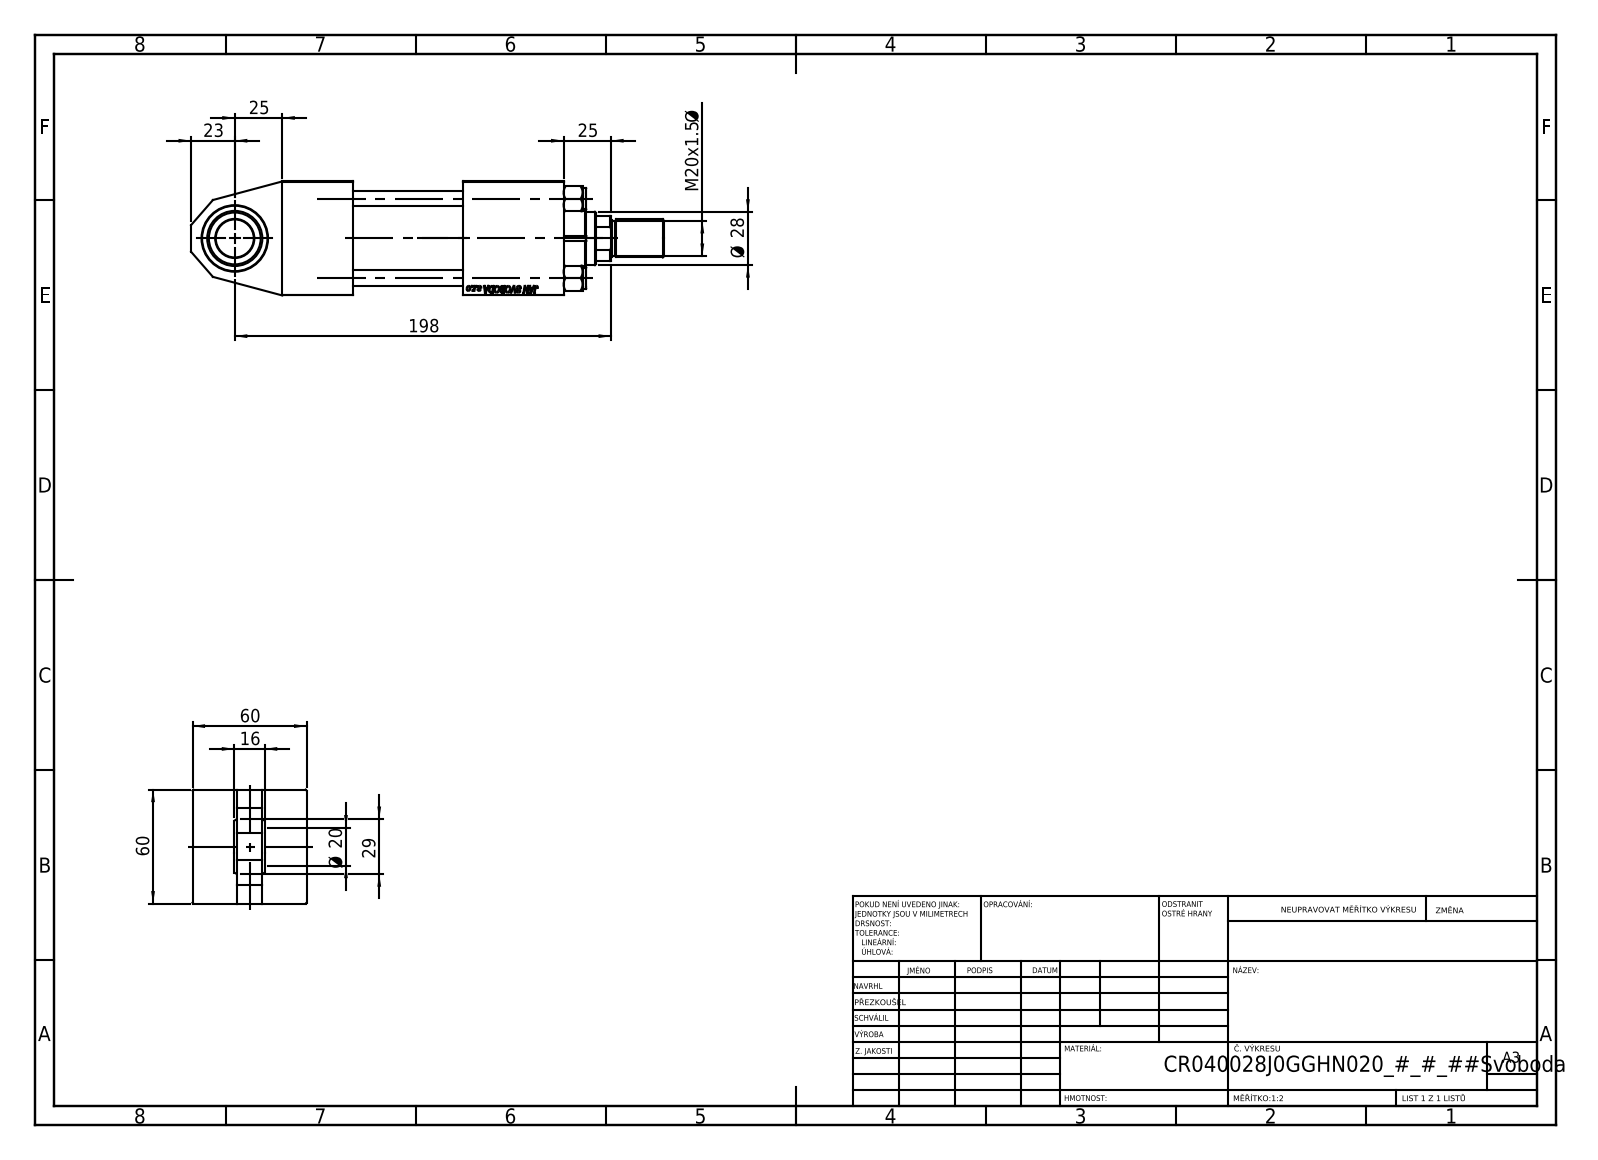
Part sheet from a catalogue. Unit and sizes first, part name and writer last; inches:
Units: inches
Overall size (bounding box): 9.803 × 2.362 × 2.362
Round holes (diameter × count): ⌀0.315 ×4, ⌀0.098 ×2, ⌀0.276 ×2, ⌀0.656 ×2, ⌀0.945 ×2, ⌀0.728 ×1, ⌀0.787 ×1, ⌀1.102 ×1, ⌀1.22 ×1, ⌀1.378 ×1, ⌀1.575 ×1, ⌀1.772 ×1
Round bosses / shafts (diameter × count): ⌀0.433 ×4, ⌀1.811 ×1, ⌀1.654 ×1, ⌀0.787 ×1, ⌀0.709 ×1
Partial cylindrical surfaces — rounded edges, fillets, slot ends (radius × count): R0.531 ×1
Main face-to-face distances: 2.362, 1.437, 0.925, 1.457, 2.087, 2.283, 3.74, 0.512, 5.827, 4.37
Hole centre spacings: 0.821, 1.161, 1.642, 1.832, 0.817, 2.322, 1.634, 3.642
Volume: 28.06 in³ · Surface area: 190.9 in²
Bodies: 13 solids, 1161 faces (523 planar, 92 cylindrical, 546 other)
Part name (STEP PRODUCT): ROD_END_AH; V215CR_J_Body; V215CR_TYCINKA_J; V215CR_J_VNITRNI_KROUZEK (+3 more)
STEP written by: SolidWorks 2019 (CONFIG_CONTROL_DESIGN)
